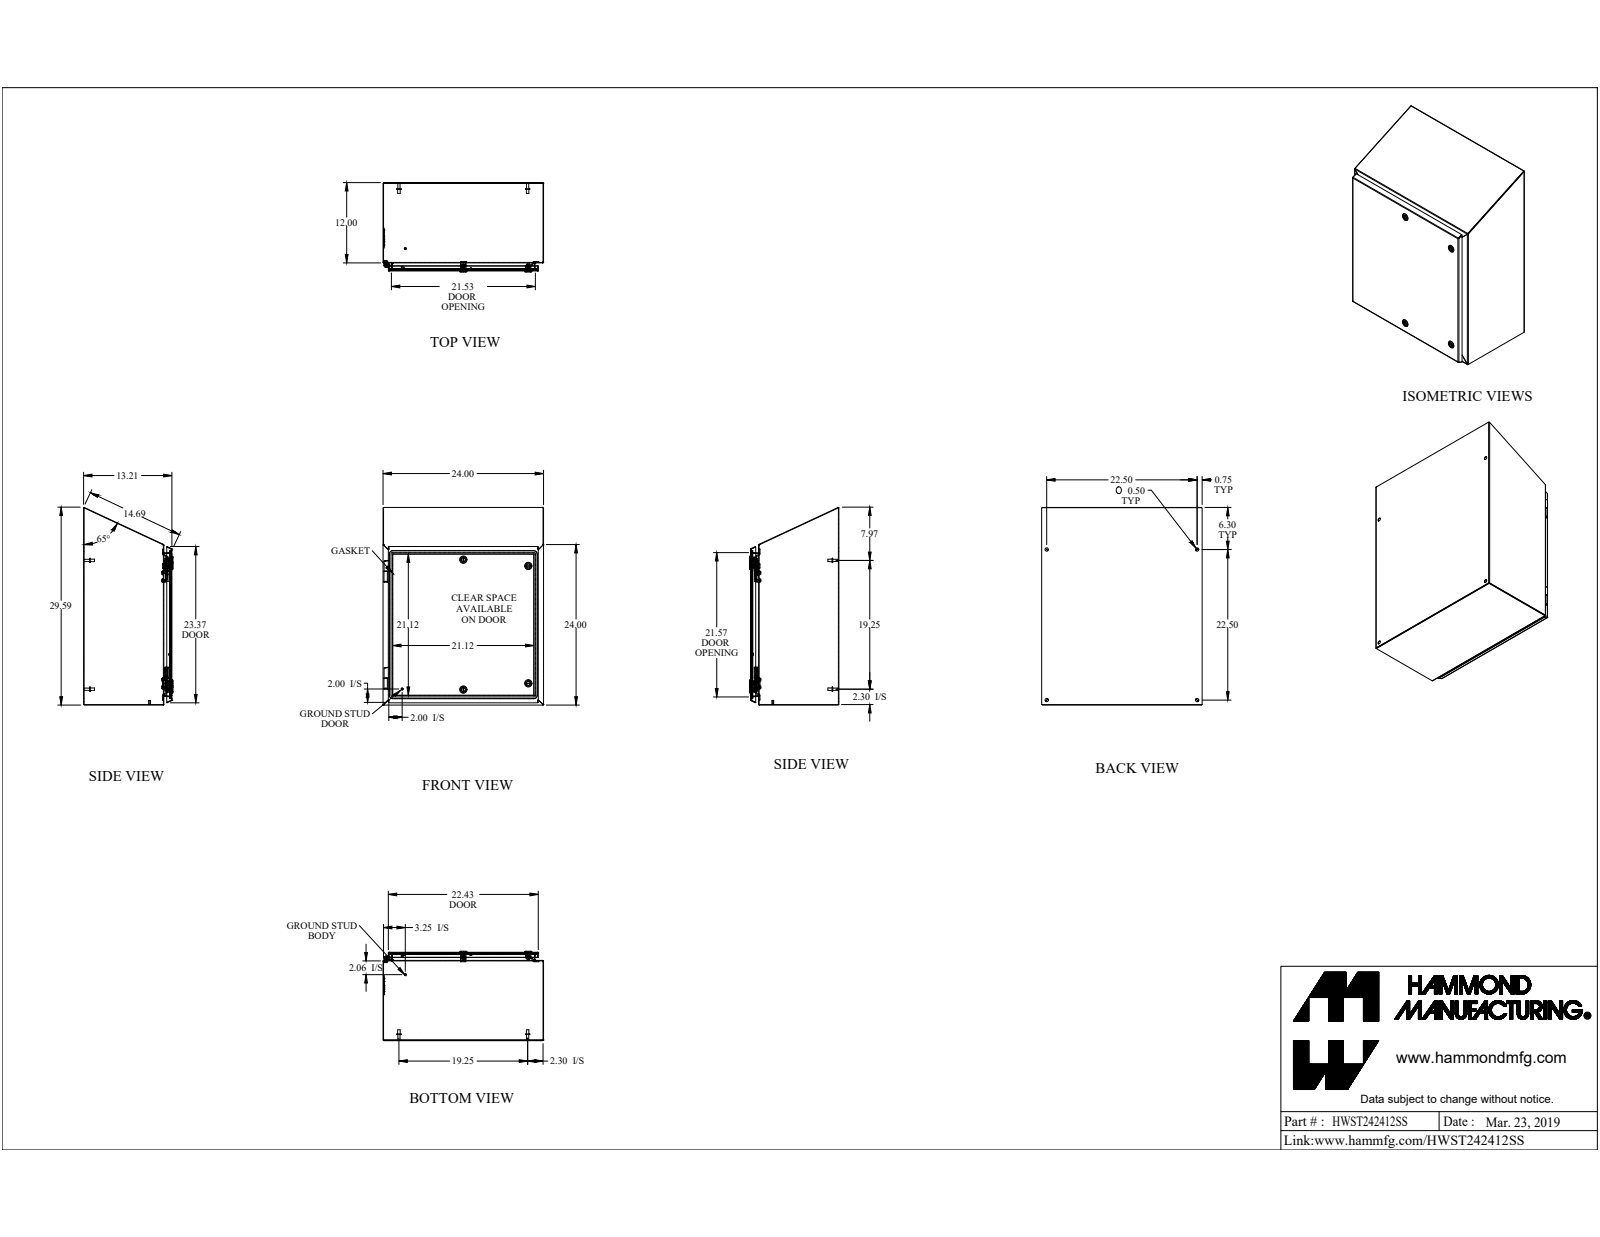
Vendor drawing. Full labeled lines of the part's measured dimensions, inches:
Part name (STEP PRODUCT): HWST242412S16
STEP written by: SolidWorks 2019 (AUTOMOTIVE_DESIGN)
Units: inches
Bodies: 54 solids, 1307 faces (807 planar, 340 cylindrical, 160 other)
Overall size (bounding box): 29.545 × 24 × 13.37
Volume: 217.3 in³ · Surface area: 5 908 in²
Round holes (diameter × count): ⌀0.194 ×8, ⌀0.24 ×8, ⌀0.5 ×8, ⌀0.197 ×4, ⌀0.275 ×4, ⌀0.387 ×4, ⌀0.63 ×4, ⌀0.768 ×4, ⌀0.13 ×2, ⌀0.24 ×1, ⌀3.5 ×1
Round bosses / shafts (diameter × count): ⌀0.226 ×8, ⌀0.625 ×6, ⌀0.236 ×5, ⌀1.1 ×4, ⌀0.65 ×4, ⌀0.525 ×4, ⌀0.375 ×4, ⌀0.332 ×4
Partial cylindrical surfaces — rounded edges, fillets, slot ends (radius × count): R0.25 ×24, R0.036 ×18, R0.108 ×18, R0.039 ×16, R0.125 ×16, R0.03 ×14, R0.012 ×12, R0.133 ×6
Main face-to-face distances: 0.072, 0.072, 23.928, 13.066, 13.138, 13.138, 13.21, 23.856, 24, 11.928
Hole centre spacings: 1.142, 15.974, 22.5, 9.76, 14.833, 15.979, 17.116, 17.634
